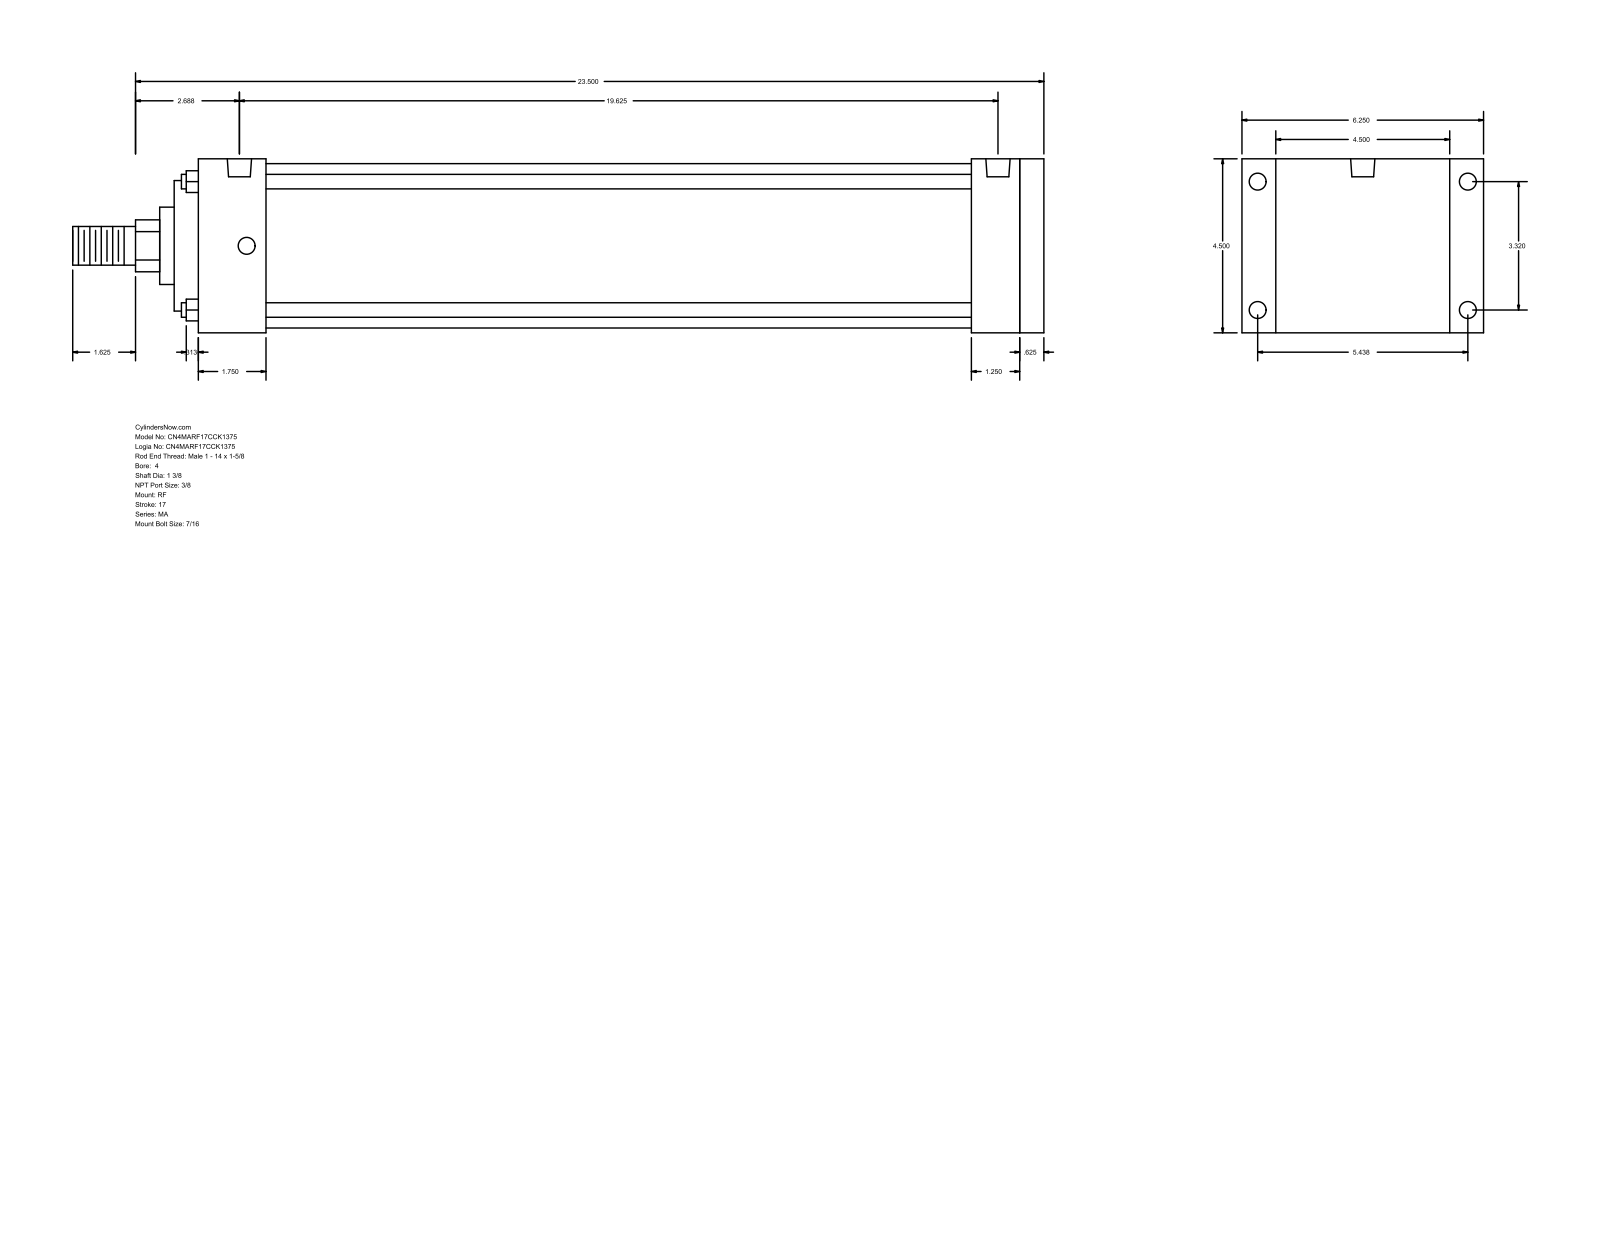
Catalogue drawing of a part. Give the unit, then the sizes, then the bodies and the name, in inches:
Units: inches
Overall size (bounding box): 25.125 × 6.25 × 4.5
Round holes (diameter × count): ⌀0.437 ×8, ⌀0.627 ×2
Round bosses / shafts (diameter × count): ⌀0.375 ×4, ⌀4.25 ×1, ⌀3.375 ×1, ⌀2 ×1, ⌀1.375 ×1, ⌀1 ×1
Partial cylindrical surfaces — rounded edges, fillets, slot ends (radius × count): R0.672 ×1
Main face-to-face distances: 4.5, 21.875, 0.625, 21.25, 0.625, 21.875, 22.5, 0.875, 5.375, 20.625
Hole centre spacings: 3.32, 5.438, 6.371, 19.25, 0.187, 0.188, 19.437, 19.438
Bodies: 0 solids, 94 faces (65 planar, 29 cylindrical, 0 other)
Part name (STEP PRODUCT): MA_RF__0400_1.375
STEP written by: GSSL Pune (CONFIG_CONTROL_DESIGN)
